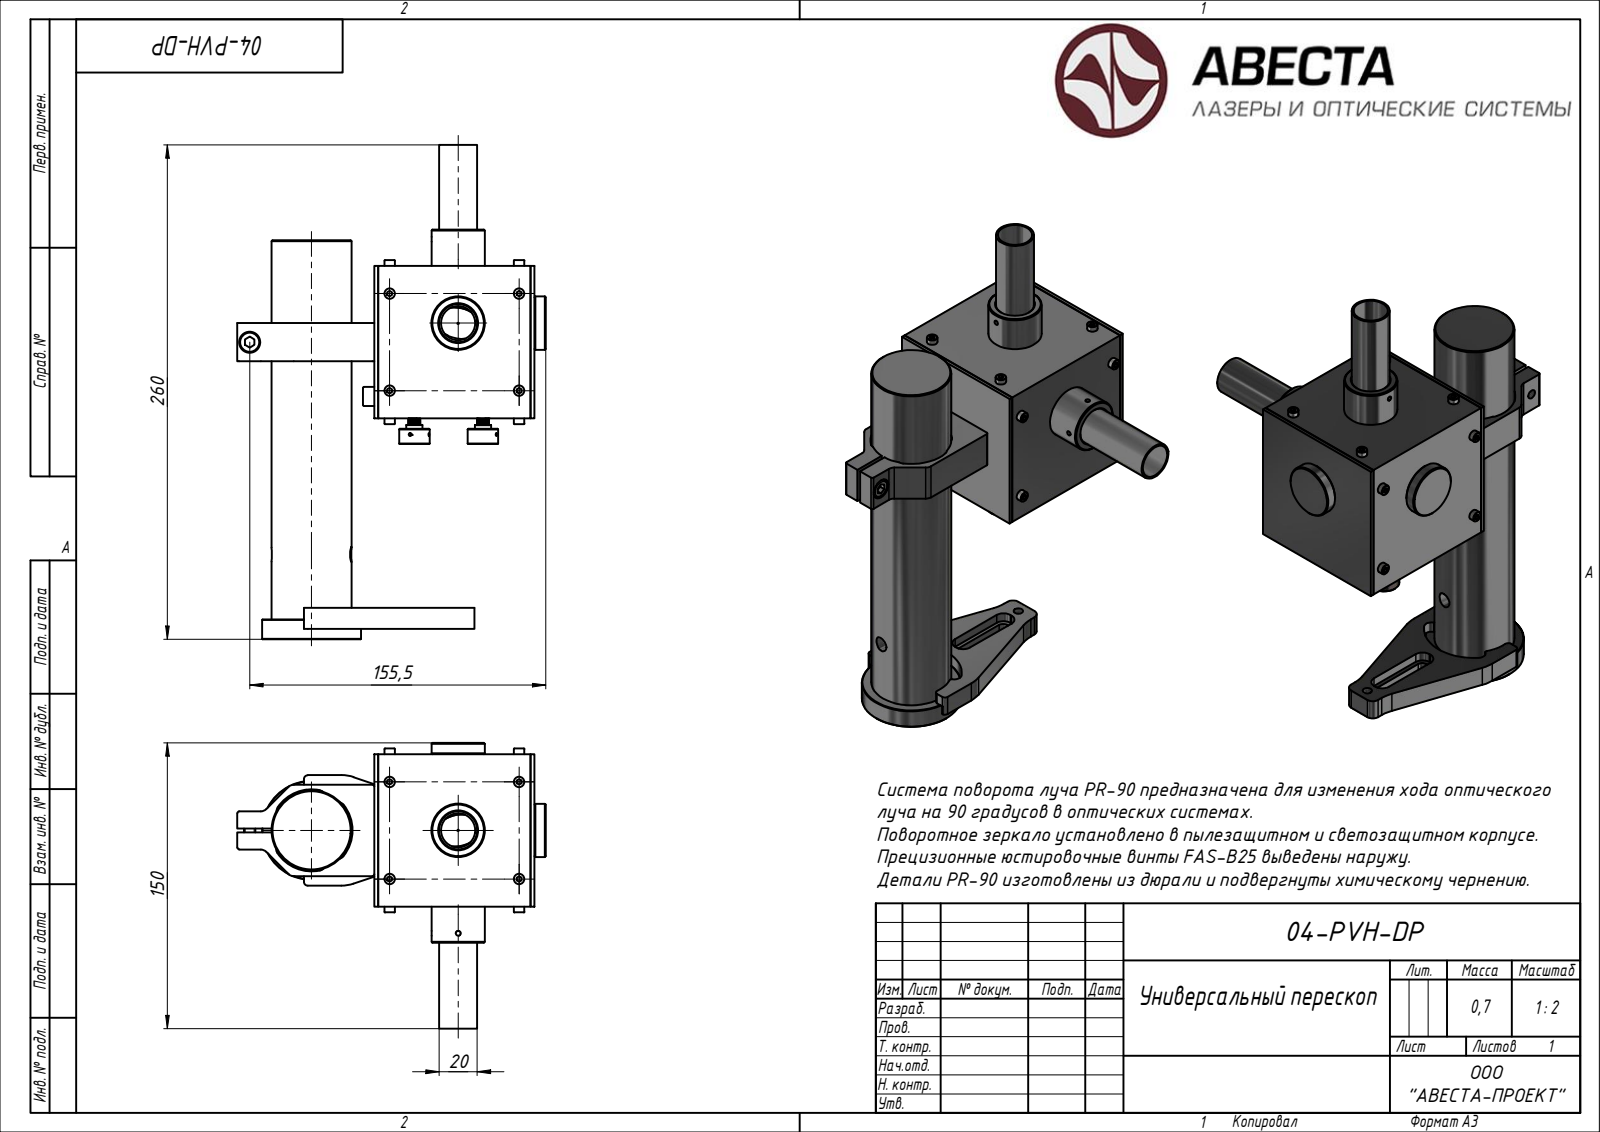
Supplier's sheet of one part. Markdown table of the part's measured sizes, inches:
| quantity | value |
| --- | --- |
| part name | 04-PR-90_Shrinkwrap_1 |
| STEP written by | Autodesk Inventor 2019 (AUTOMOTIVE_DESIGN) |
| units | inches |
| bodies | 14 solids, 1076 faces (451 planar, 365 cylindrical, 260 other) |
| overall size | 10.216 × 6.378 × 5.906 |
| volume | 37.95 in³ |
| surface area | 235.1 in² |
| round holes (diameter × count) | 0.194 × 8, 0.315 × 5, 0.256 × 4, 0.433 × 4, 0.11 × 3, 0.236 × 3, 0.079 × 2, 0.097 × 2, 0.098 × 2, 0.122 × 2, 0.354 × 2, 0.709 × 2 |
| round bosses / shafts (diameter × count) | 0.217 × 8, 0.236 × 4, 0.062 × 4, 1.102 × 3, 0.945 × 2, 0.787 × 2, 0.63 × 2, 0.394 × 2 |
| partial cylindrical surfaces (radius × count) | 0.157 × 13, 0.039 × 8, 0.197 × 8, 0.079 × 4, 0.118 × 4, 0.787 × 4, 0.571 × 1, 0.835 × 1 |
| main face-to-face distances | 2.992, 0.157, 3.15, 0.433, 2.835, 0.551, 2.756, 3.307, 2.323, 2.874 |
| hole center spacings | 0.61, 1.417, 0.371, 0.472, 0.724, 0.811, 0.906, 0.945 |
